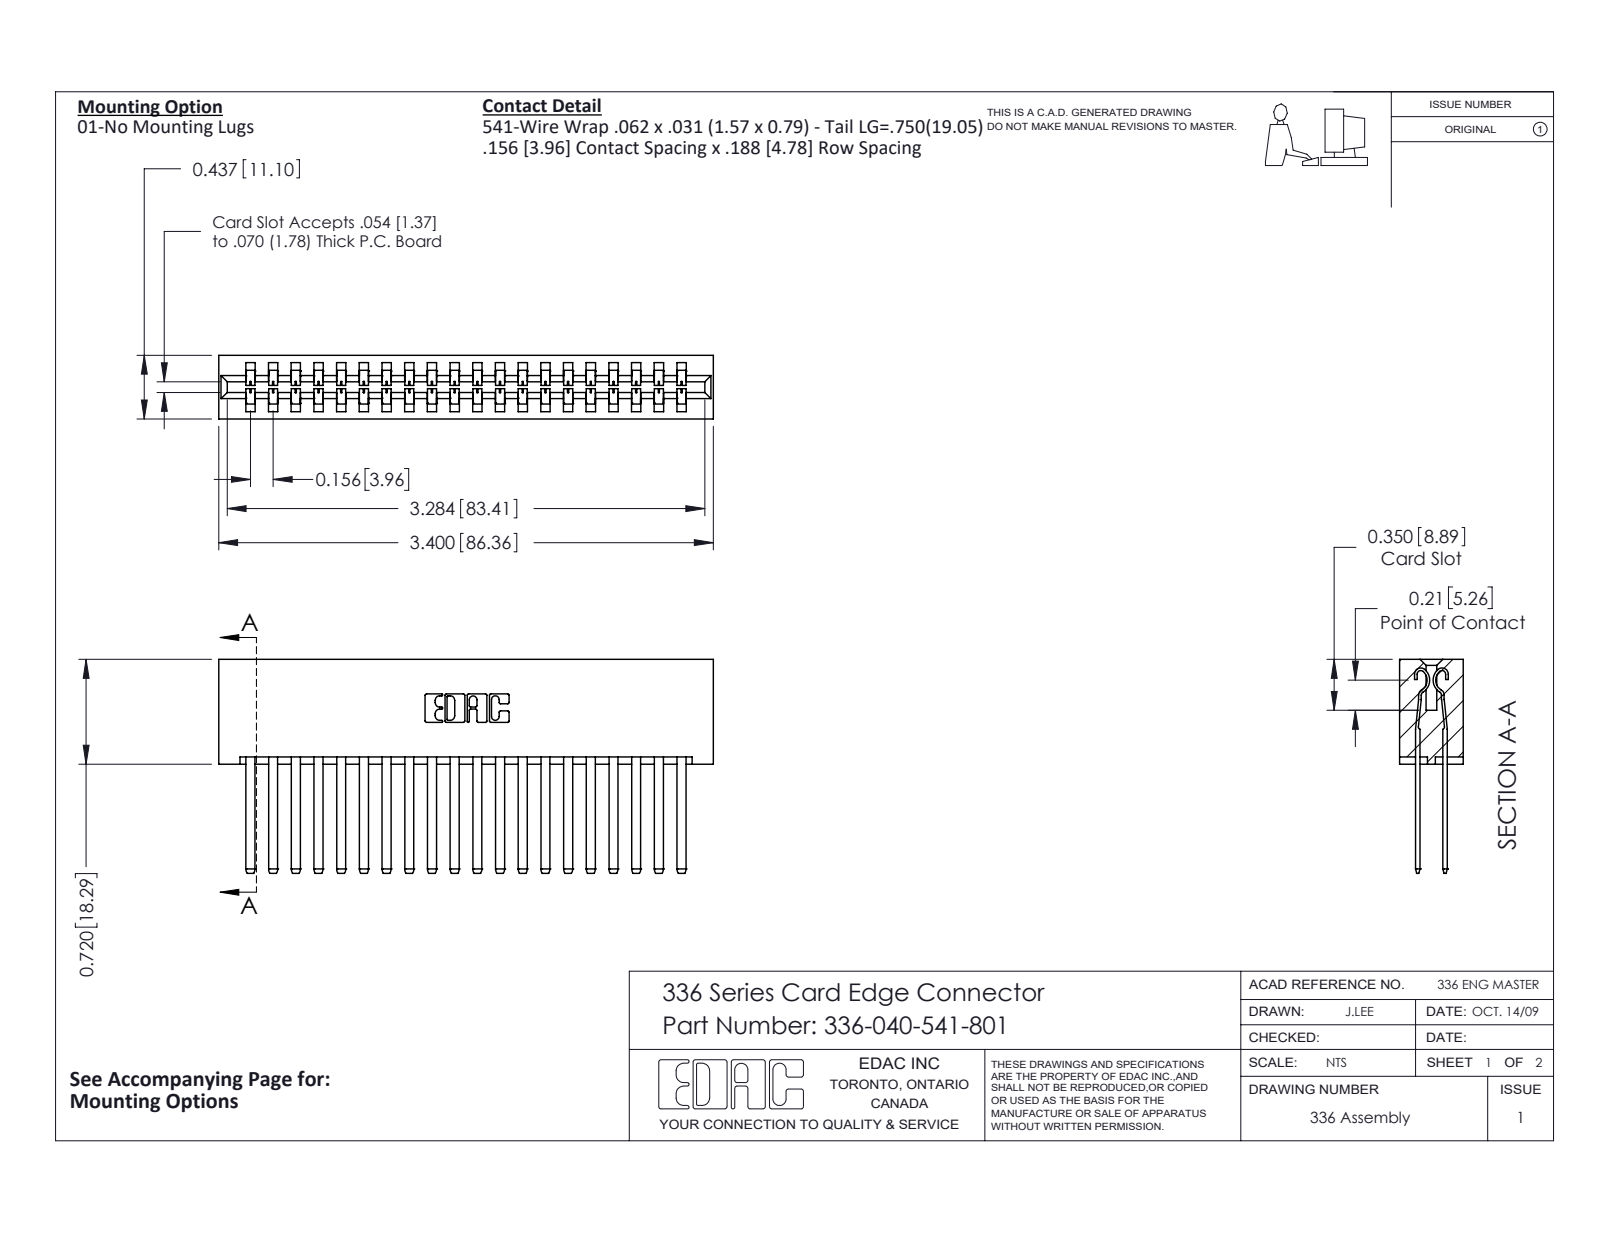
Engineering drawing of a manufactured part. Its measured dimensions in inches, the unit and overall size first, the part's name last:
Units: inches
Overall size (bounding box): 3.4 × 1.47 × 0.437
Partial cylindrical surfaces — rounded edges, fillets, slot ends (radius × count): R0.004 ×80, R0.056 ×40, R0.01 ×22, R0.007 ×6, R0.031 ×6, R0.022 ×4, R0.04 ×4, R0.026 ×3
Main face-to-face distances: 0.188, 0.328, 0.14, 0.297, 0.109, 0.031, 0.437, 0.033, 0.156, 0.181
Volume: 0.872 in³ · Surface area: 27.92 in²
Bodies: 41 solids, 1786 faces (1106 planar, 680 cylindrical, 0 other)
Part name (STEP PRODUCT): 336 Part_Lugless; 336-290-001_336-290-541; 336-040-541-801
STEP written by: SolidWorks 2020 (CONFIG_CONTROL_DESIGN)
